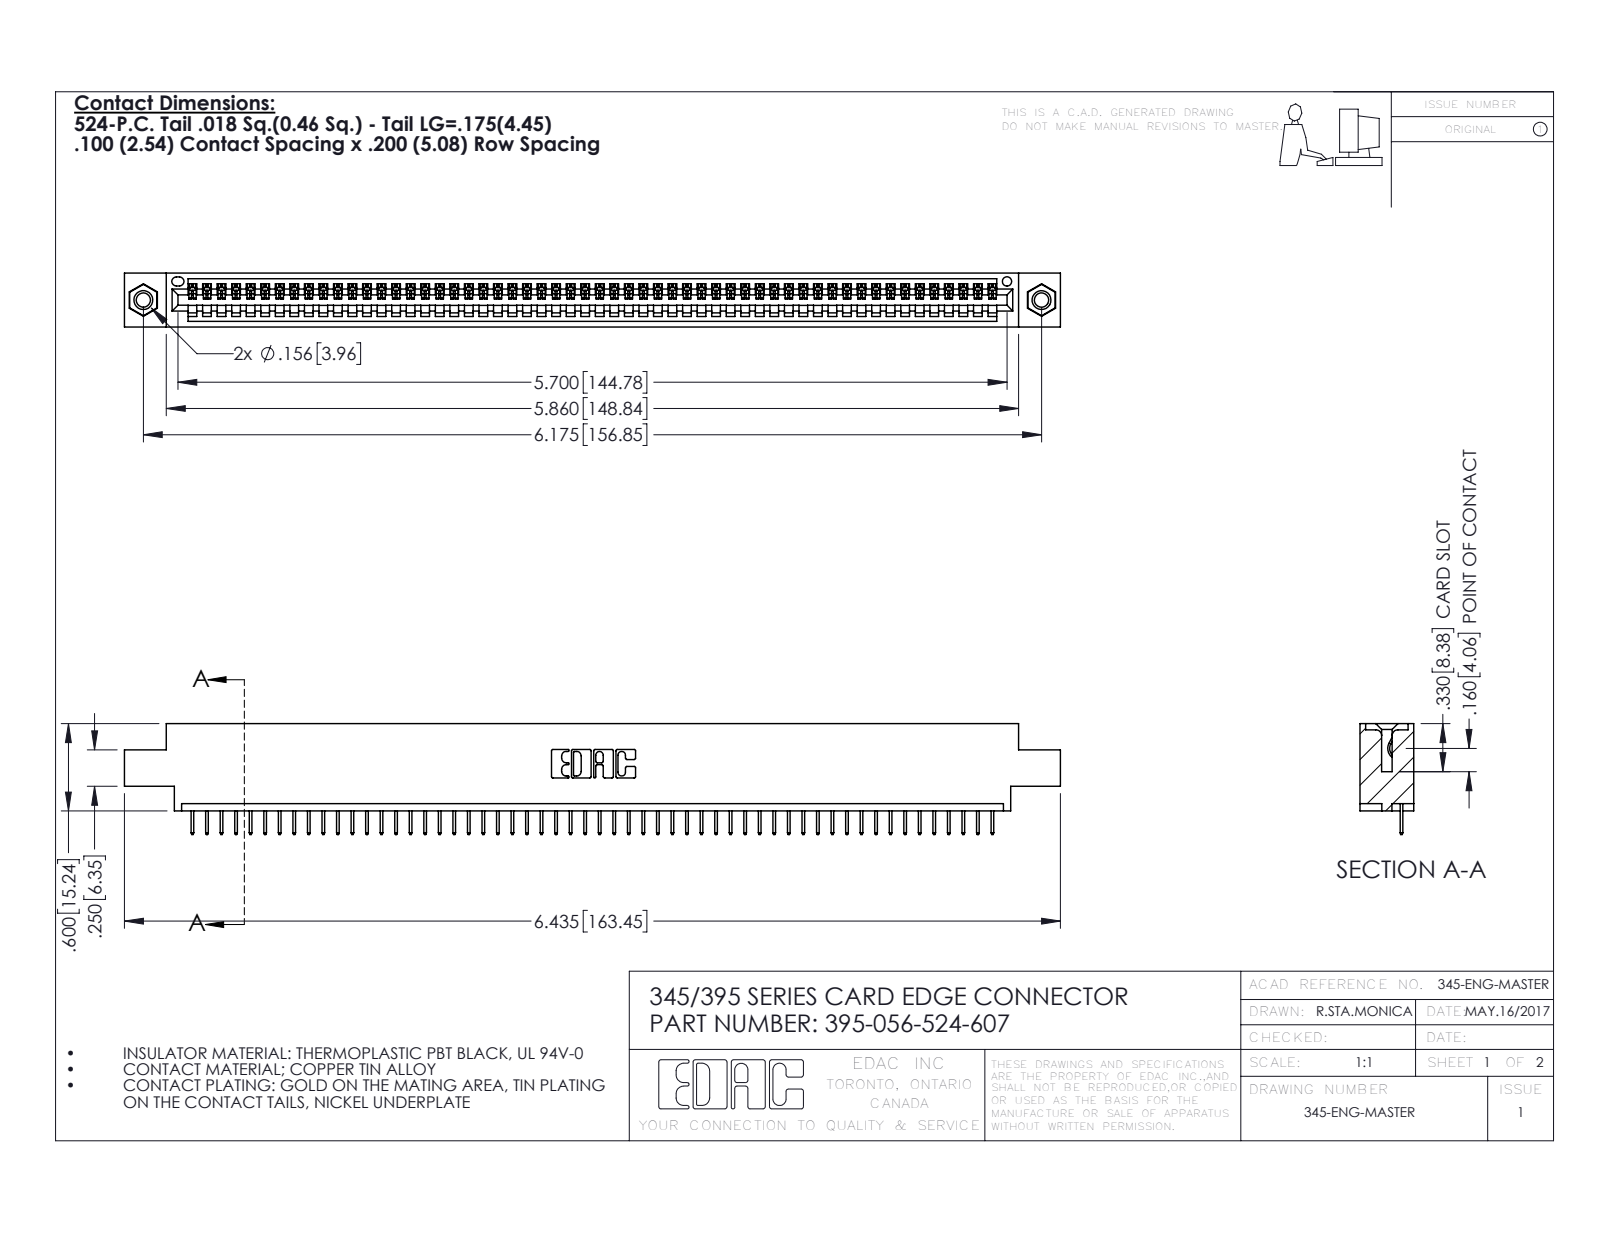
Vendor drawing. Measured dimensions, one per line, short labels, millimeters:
name: 345 Part_0.170 Offset - 0.156 Dia-TI; 395-056-524-607; 345-250-001_345-250-005-103; 345-292-001_345-293-124
written by: SolidWorks 2016 (CONFIG_CONTROL_DESIGN)
unit: mm
bodies: 59 solids, 3662 faces (2692 planar, 954 cylindrical, 16 other)
size: 163.4 × 19.4 × 9.4
volume: 15 300 mm³; area: 19 960 mm²
holes: 2× ⌀2.5, 2× ⌀3.2, 2× ⌀4, 1× ⌀1.6
bosses: 2× ⌀3.9
rounds: 112× R0.2, 22× R0.3, 6× R0.2, 6× R0.8, 3× R0.7, 2× R0.8, 2× R1, 1× R0.4
face distances: 1.8, 7.6, 9.4, 5.1, 2.5, 6.9, 0.6, 5.7, 1.8, 4.4
hole spacings: 6.9, 150.9, 156.8
